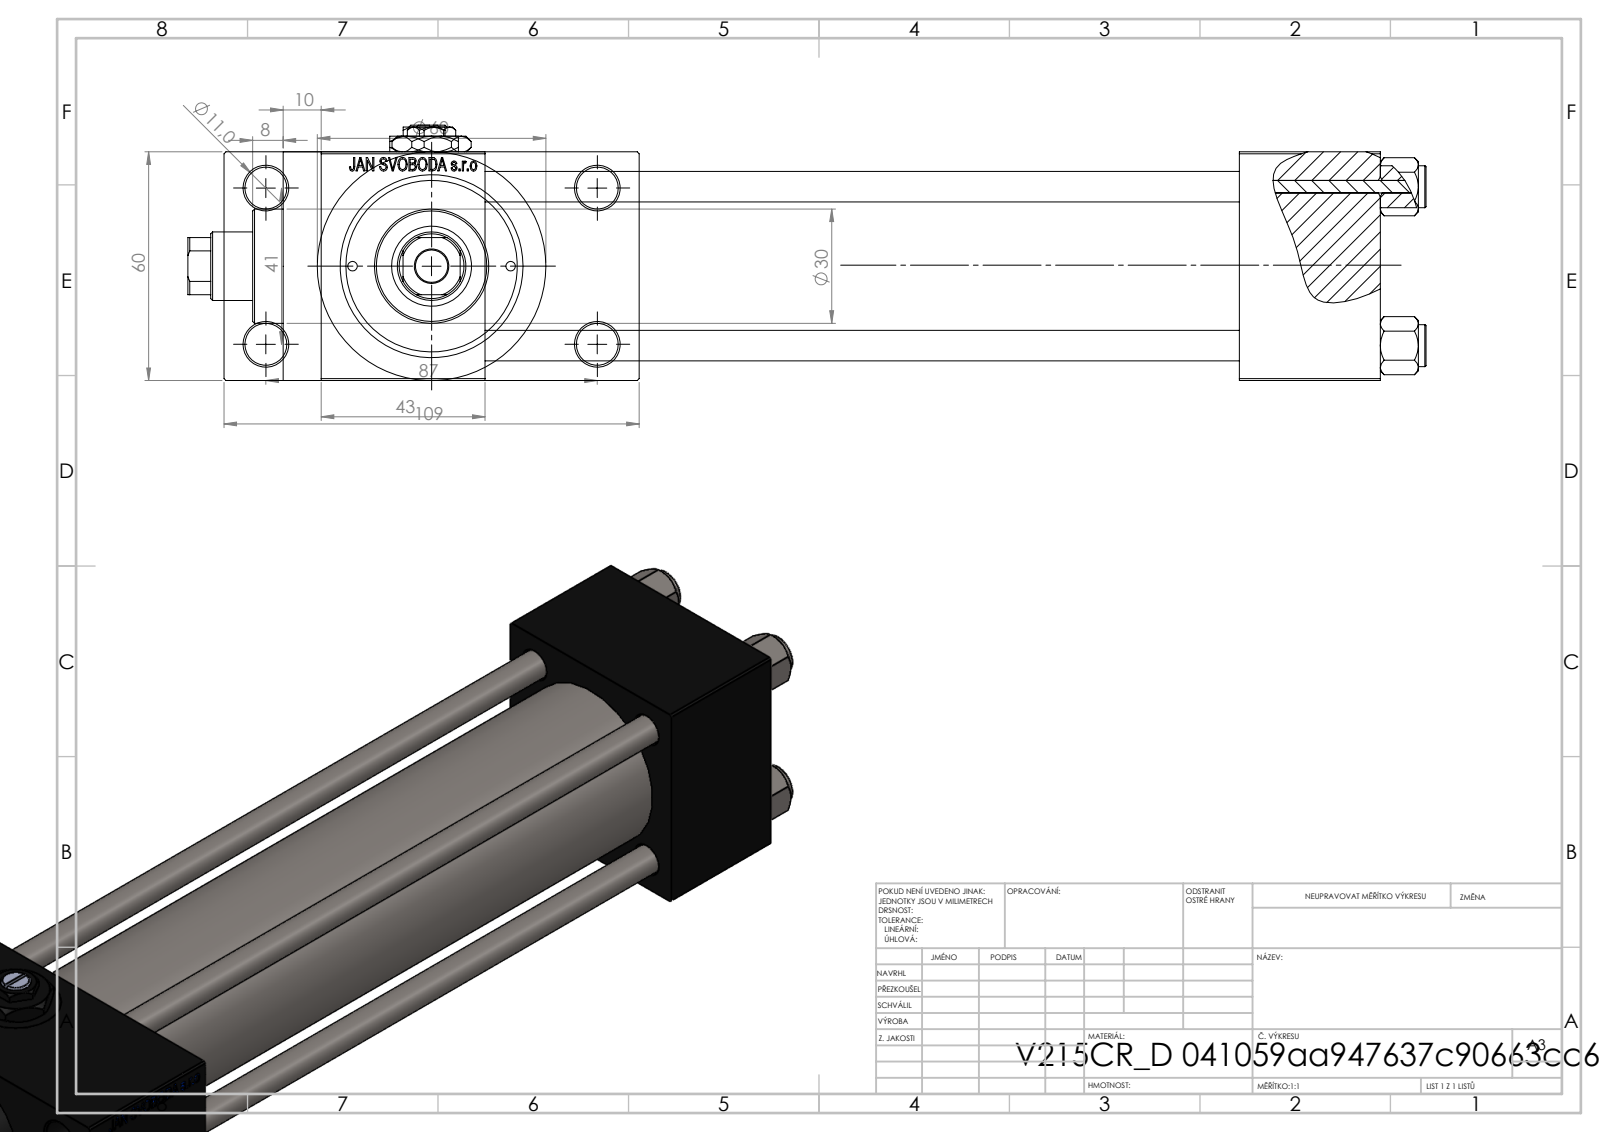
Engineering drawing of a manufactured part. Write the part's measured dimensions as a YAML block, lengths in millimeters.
part_name: "V215CR_D_TYCINKA; NUT_M5_D; V215CR_D_Body; V215CR_VCP_D (+2 more)"
step_written_by: "SolidWorks 2019 (CONFIG_CONTROL_DESIGN)"
units: millimeters
bodies: {solids: 12, faces: 1160, planar: 524, cylindrical: 96, other: 540}
overall_size: [325, 109, 67]
volume: 632388
surface_area: 183231
round_holes:
  - {diameter: 8, count: 4}
  - {diameter: 11, count: 4}
  - {diameter: 16.66, count: 3}
  - {diameter: 24, count: 3}
  - {diameter: 2.5, count: 2}
  - {diameter: 7, count: 2}
  - {diameter: 8.5, count: 1}
  - {diameter: 18, count: 1}
  - {diameter: 21, count: 1}
  - {diameter: 31, count: 1}
  - {diameter: 40, count: 1}
  - {diameter: 45, count: 1}
round_bosses_or_shafts:
  - {diameter: 11, count: 4}
  - {diameter: 60, count: 1}
  - {diameter: 46, count: 1}
  - {diameter: 30, count: 1}
partial_cylinders:
  - {radius: 8.5, count: 1}
face_to_face_distances: [60, 198, 24.5, 84.5, 37, 235, 43, 278, 241, 10]
hole_center_spacings: [20.85, 22.65, 29.49, 30.62, 41.7, 46.53, 47.15, 48.09]
